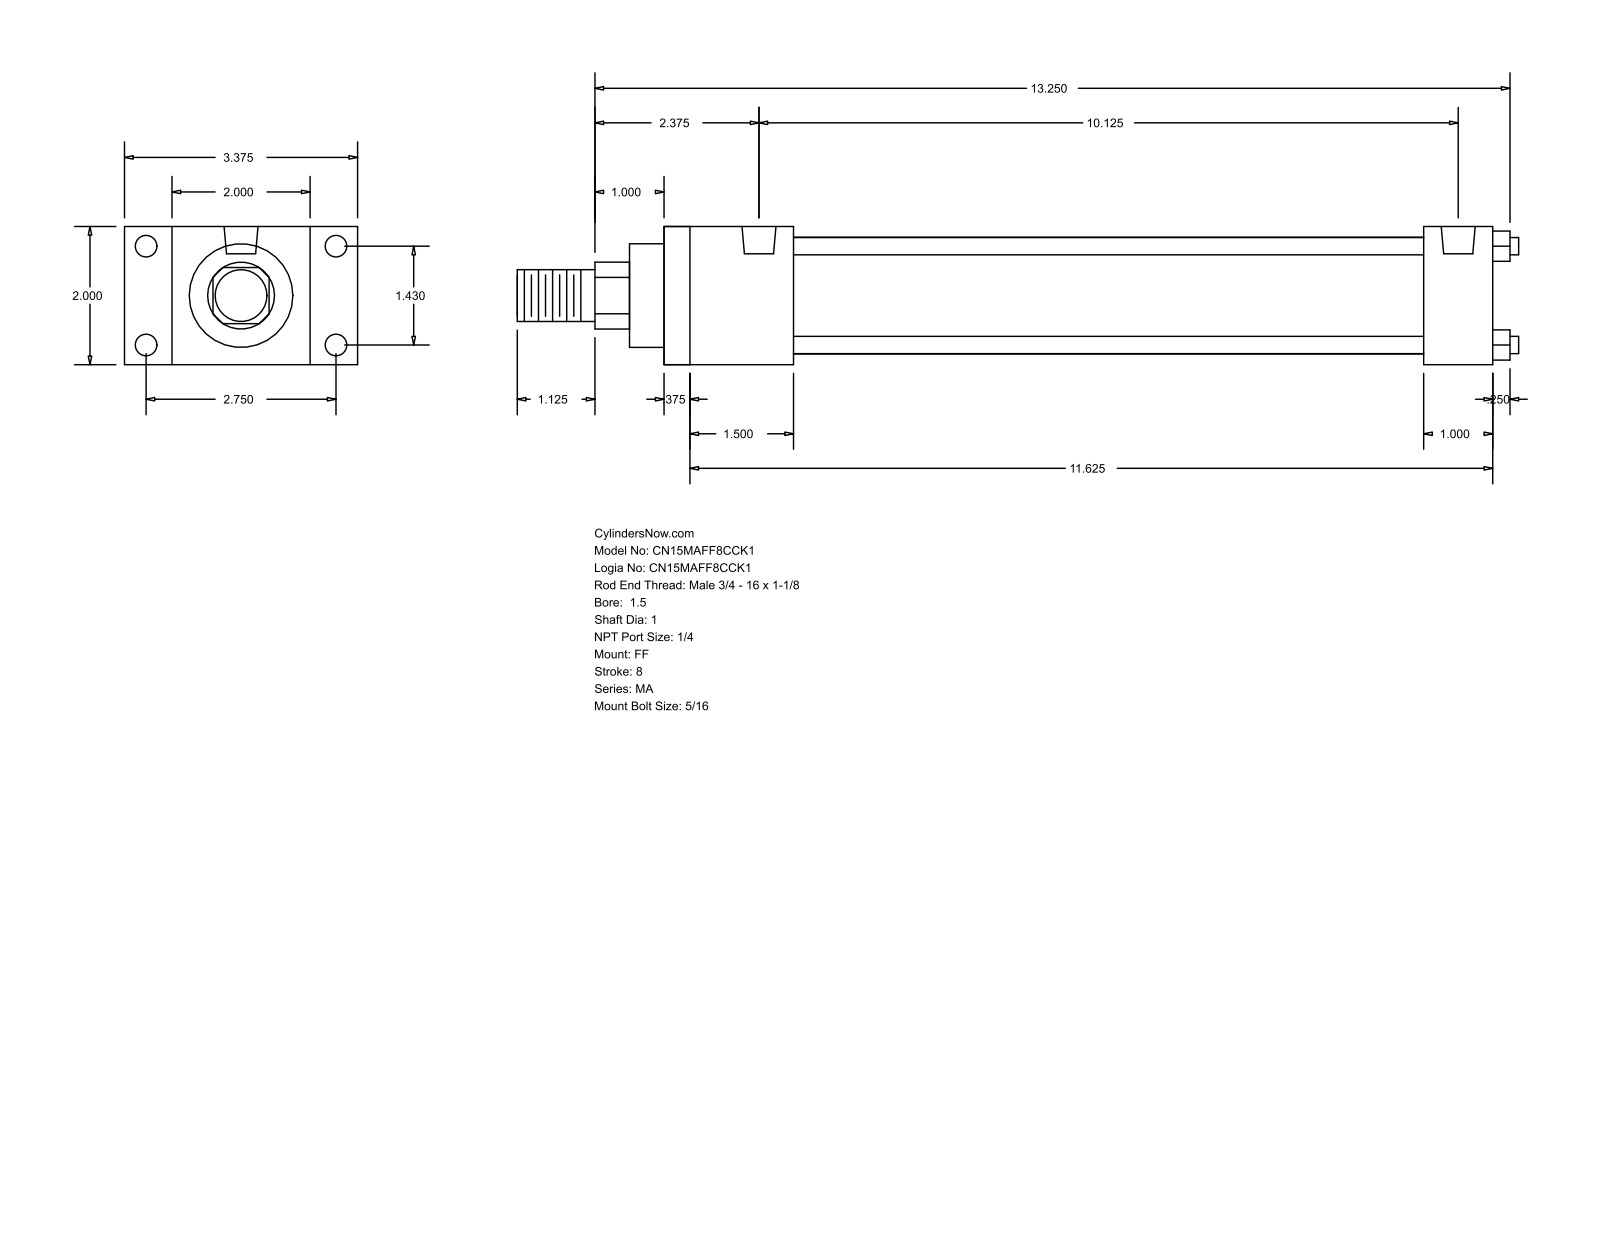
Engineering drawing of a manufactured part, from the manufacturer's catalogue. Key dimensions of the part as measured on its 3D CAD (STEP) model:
Part name (STEP PRODUCT): MA_FF__0150_1
STEP written by: GSSL Pune (CONFIG_CONTROL_DESIGN)
Units: millimetres
Bodies: 0 solids, 92 faces (64 planar, 28 cylindrical, 0 other)
Overall size (bounding box): 368.3 × 85.72 × 50.8
Round holes (diameter × count): ⌀7.94 ×8, ⌀12.49 ×2
Round bosses / shafts (diameter × count): ⌀6.35 ×4, ⌀42.93 ×1, ⌀38.1 ×1, ⌀25.4 ×1, ⌀19.05 ×1
Partial cylindrical surfaces — rounded edges, fillets, slot ends (radius × count): R12.29 ×1
Main face-to-face distances: 50.8, 304.8, 9.52, 295.28, 25.4, 47.63, 279.4, 38.11, 269.88, 231.77
Hole centre spacings: 36.32, 69.84, 78.72, 257.17
